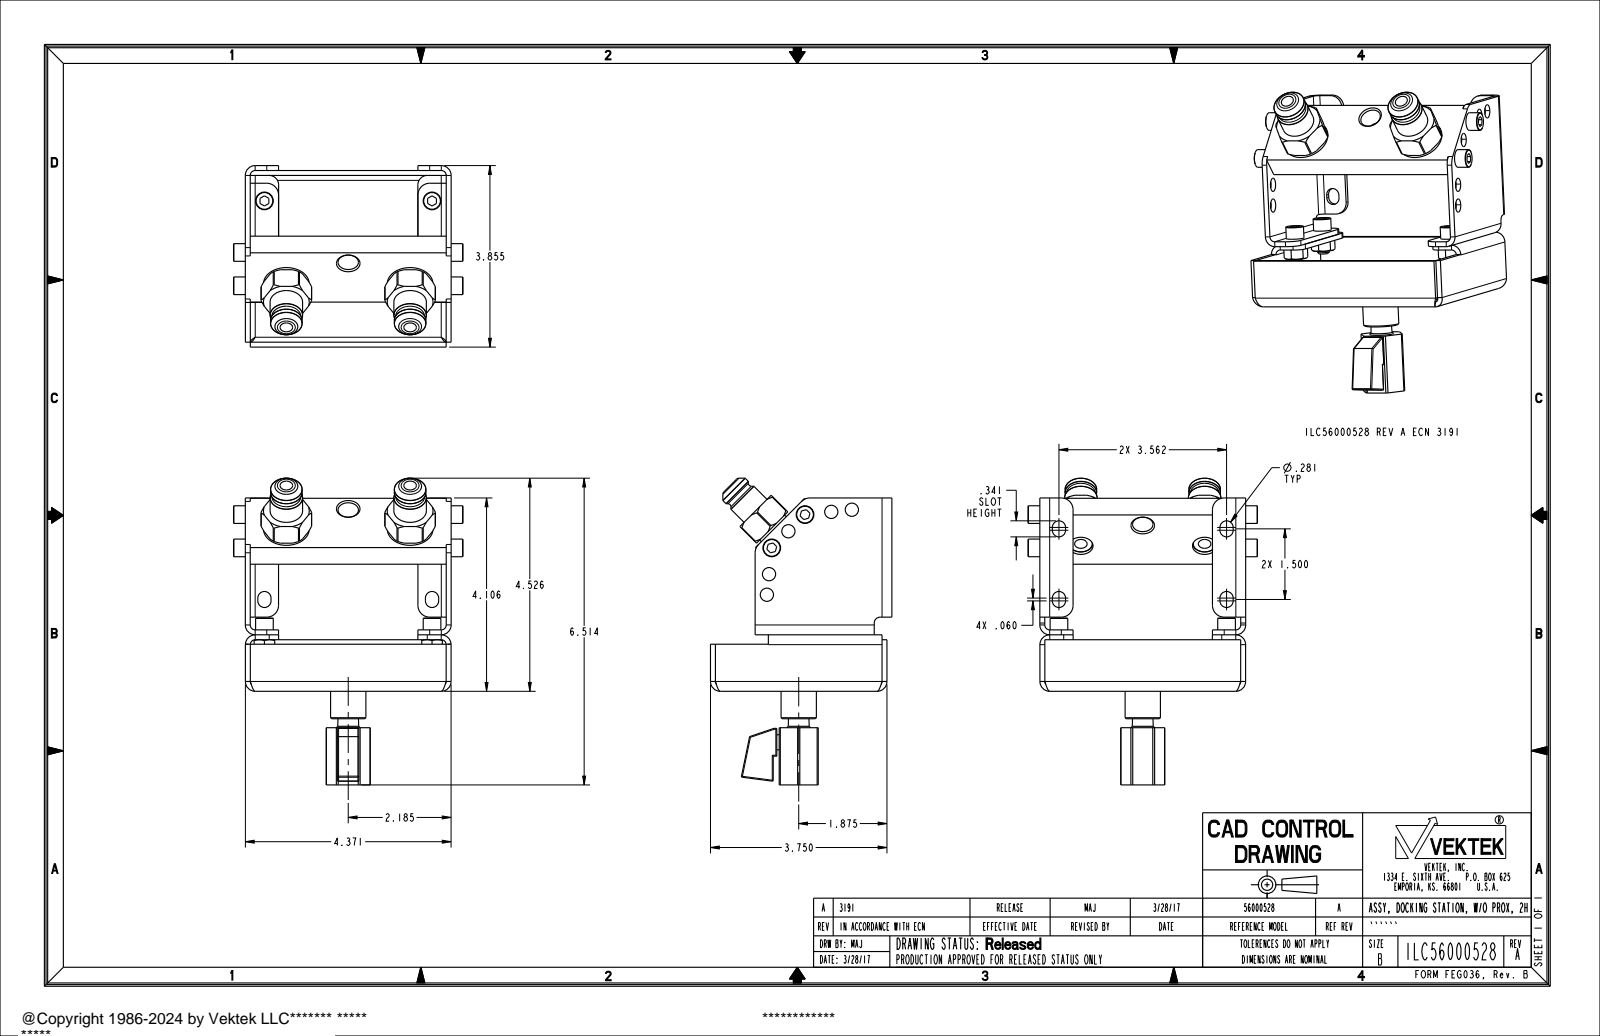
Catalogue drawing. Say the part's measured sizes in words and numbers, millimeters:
The part is named "ILC56000528". Its 3-D file was written by "PRO/ENGINEER BY PARAMETRIC TECHNOLOGY CORPORATION, 2013320 (AUTOMOTIVE_DESIGN)". It is 3 solids with 564 faces: 236 planar, 162 cylindrical and 166 other. Overall it measures 163.7 by 147.8 by 123.8 millimeters. Its volume is 180 600 cubic millimeters and its surface area 97 230 square millimeters. Round holes: 5 of diameter 7.1, 2 of diameter 6.8, 2 of diameter 13.1, 2 of diameter 24.6, 1 of diameter 8, 1 of diameter 11, 1 of diameter 11.3, 1 of diameter 19.8. Round bosses or shafts: 6 of diameter 9.5, 4 of diameter 6.4, 3 of diameter 19.1, 2 of diameter 17.5, 2 of diameter 17, 1 of diameter 8.1. Partial cylindrical surfaces (rounded edges, fillets, slot ends): 18 of radius 0.5, 10 of radius 2.7, 10 of radius 5.3, 10 of radius 6.4, 8 of radius 3.6, 4 of radius 5.1, 2 of radius 13.6, 1 of radius 3.2. The main face-to-face distances are 2.7, 108.4, 108.4, 92.6, 111.1, 2.7, 105.7, 105.8, 2.6, 111. The hole center spacings are 11.2, 25.4, 36.1, 36.8, 56.6, 47.5, 64.8, 66.8.
